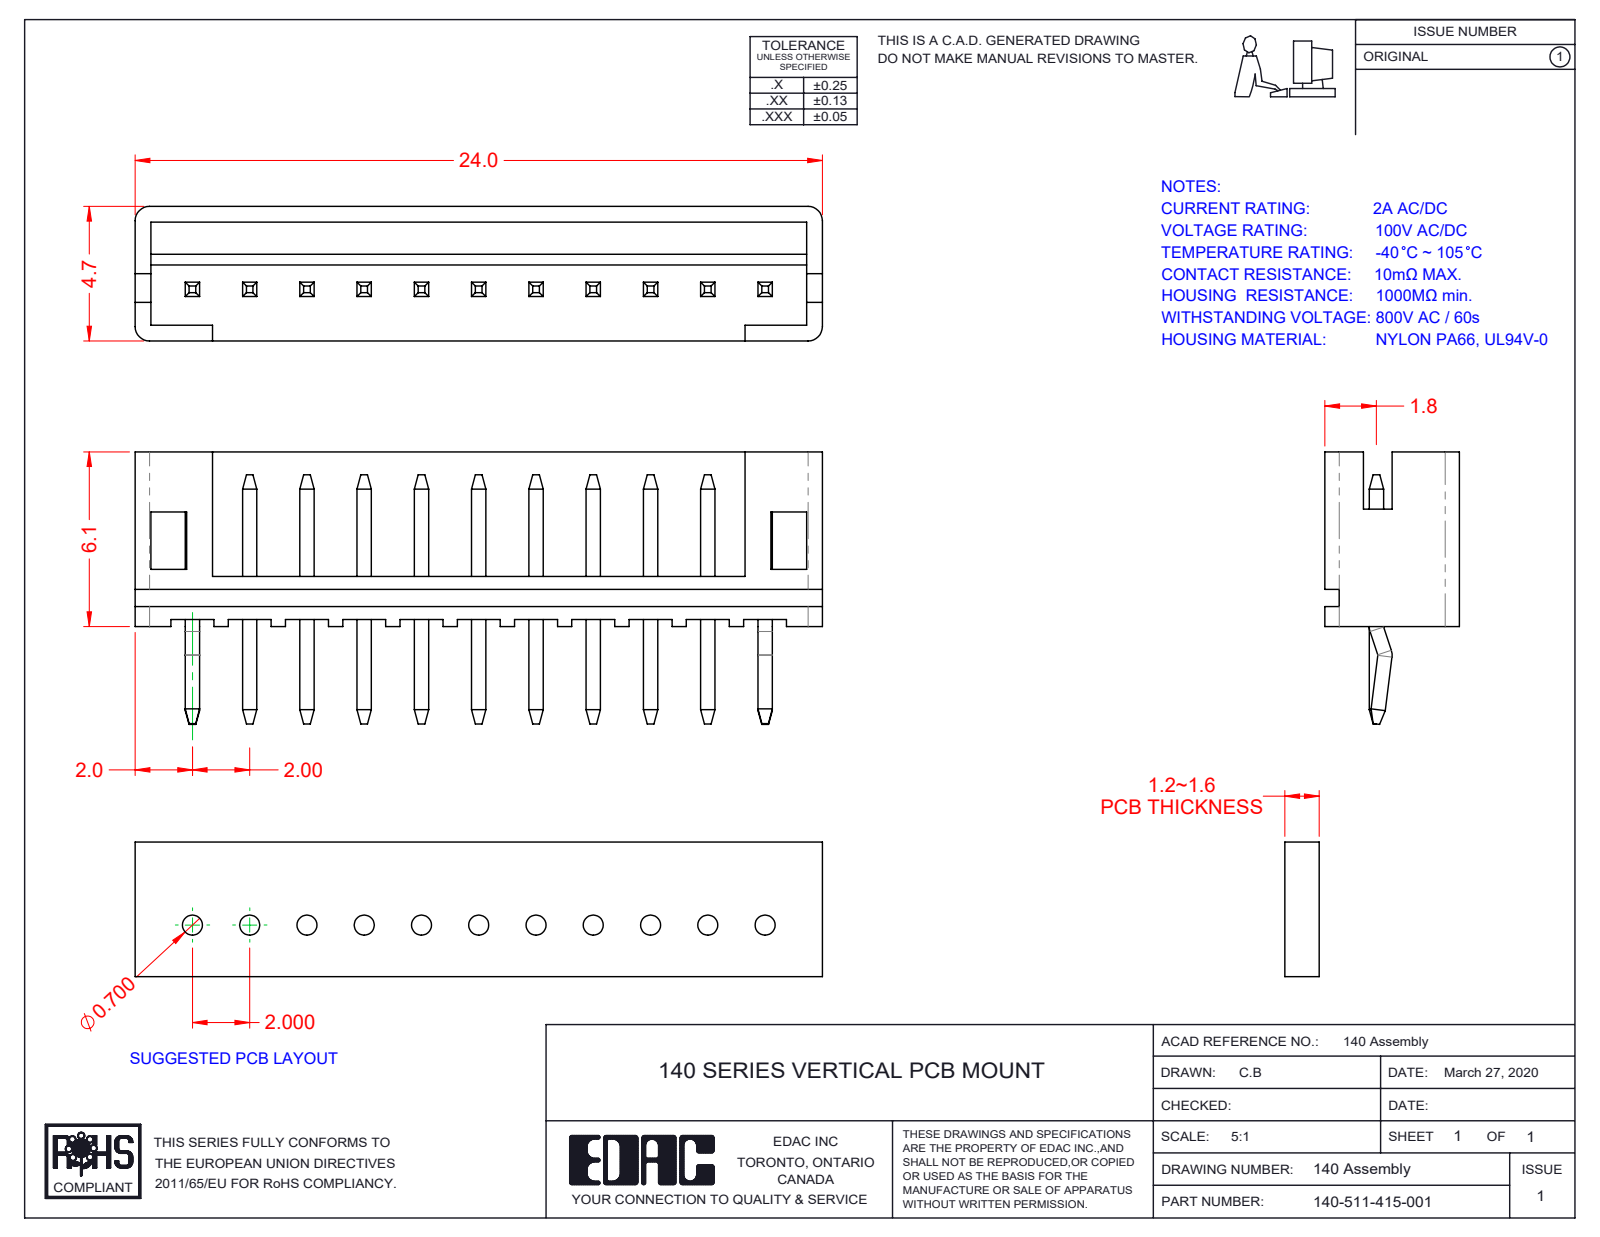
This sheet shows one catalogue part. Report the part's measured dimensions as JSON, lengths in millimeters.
{"part_name": "V Contact_Str; V Contact_Kink; 140-511-415-001; V Housing_511", "step_written_by": "SolidWorks 2016 (CONFIG_CONTROL_DESIGN)", "units": "millimeters", "bodies": {"solids": 12, "faces": 312, "planar": 294, "cylindrical": 16, "other": 2}, "overall_size": [24, 9.52, 4.7], "volume_mm3": 251, "surface_area_mm2": 918, "partial_cylinders_radius": [[0.5, 4], [0.55, 1]], "face_to_face_distances": [0.55, 1.5, 0.5, 2, 1.55, 2.1, 4.15, 4, 2.65, 1.75]}
